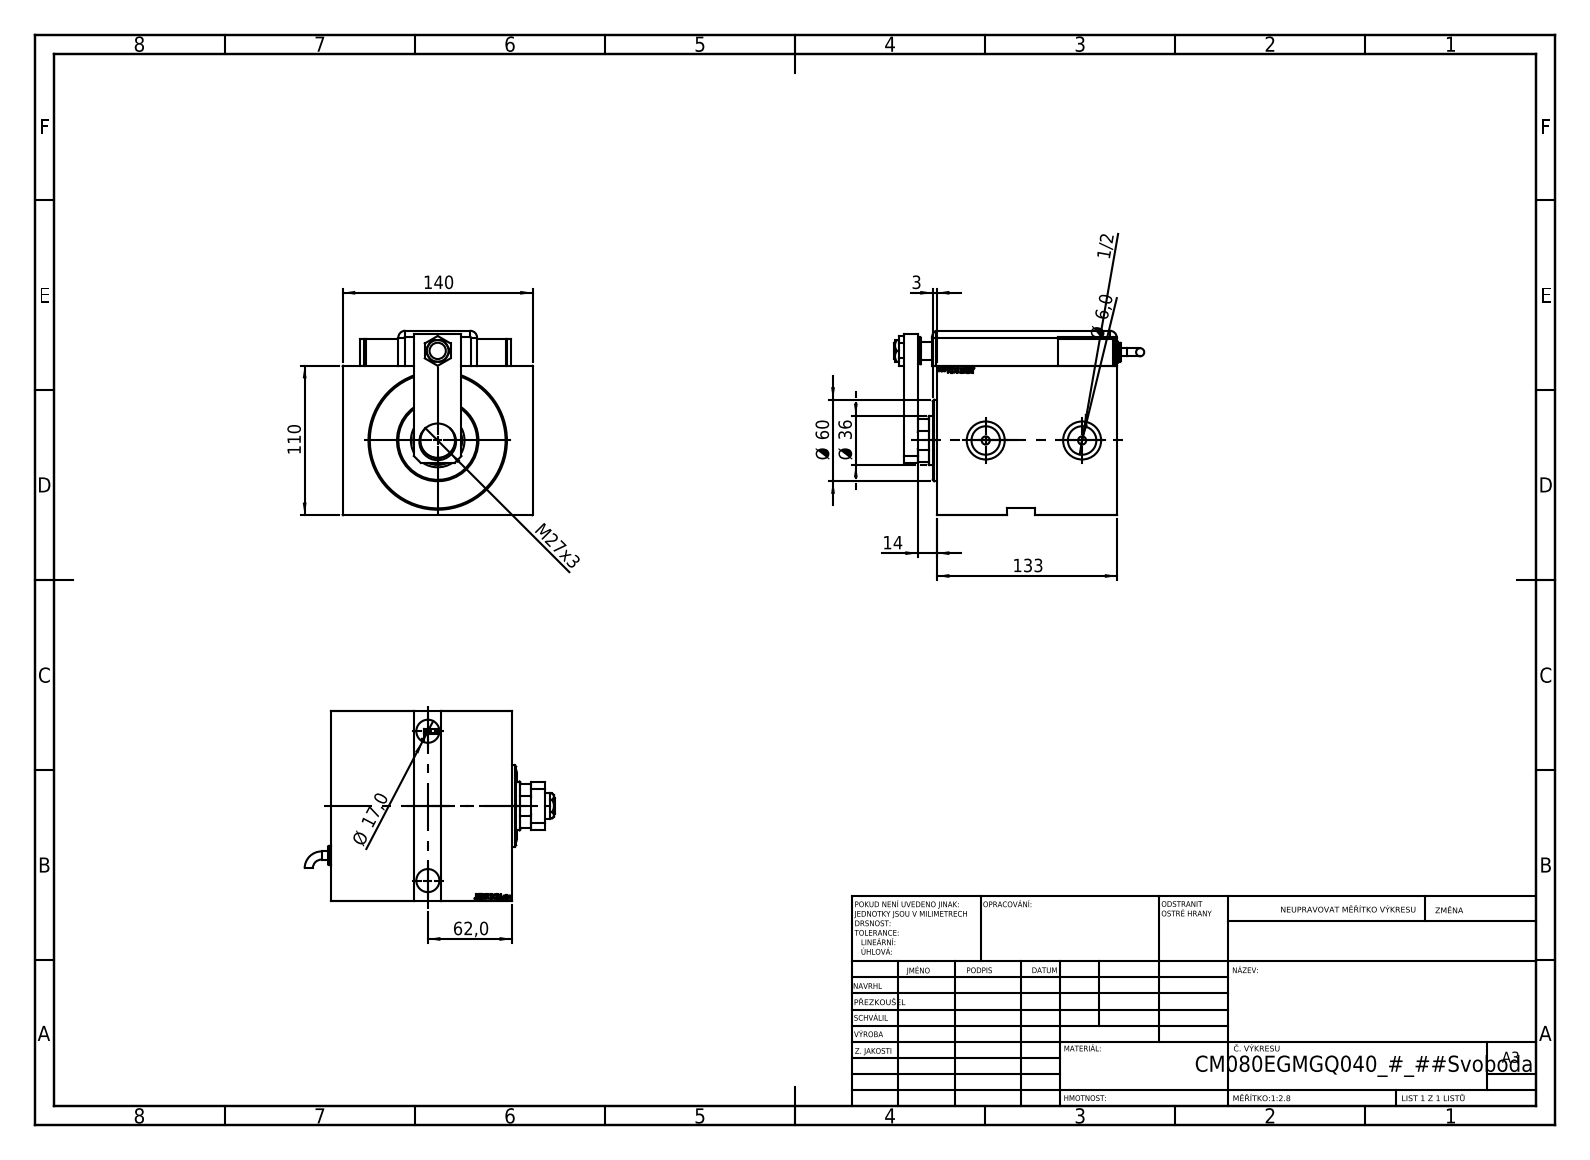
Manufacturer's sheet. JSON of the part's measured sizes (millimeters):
{"part_name": "V450CM_E_VCP; KRYT; V450CM_VC_B; ZARAZKA_Q (+7 more)", "step_written_by": "SolidWorks 2019 (CONFIG_CONTROL_DESIGN)", "units": "millimeters", "bodies": {"solids": 13, "faces": 1232, "planar": 616, "cylindrical": 99, "other": 517}, "overall_size": [184.46, 140, 135.8], "volume_mm3": 1986000, "surface_area_mm2": 261817, "round_holes": [[4, 2], [6, 2], [8, 2], [17, 2], [20.96, 2], [25, 2], [28, 2], [12, 1], [13, 1], [14, 1], [25.5, 1], [27, 1]], "round_bosses_or_shafts": [[20, 3], [16, 2], [14, 2], [6, 2], [82, 1], [60, 1]], "partial_cylinders_radius": [[5, 9], [10, 1], [17.5, 1]], "face_to_face_distances": [110, 133, 3, 140, 21, 112, 5, 128, 135.8, 25.8], "hole_center_spacings": [71.06, 85.15, 1, 20, 66, 67, 71, 110]}
